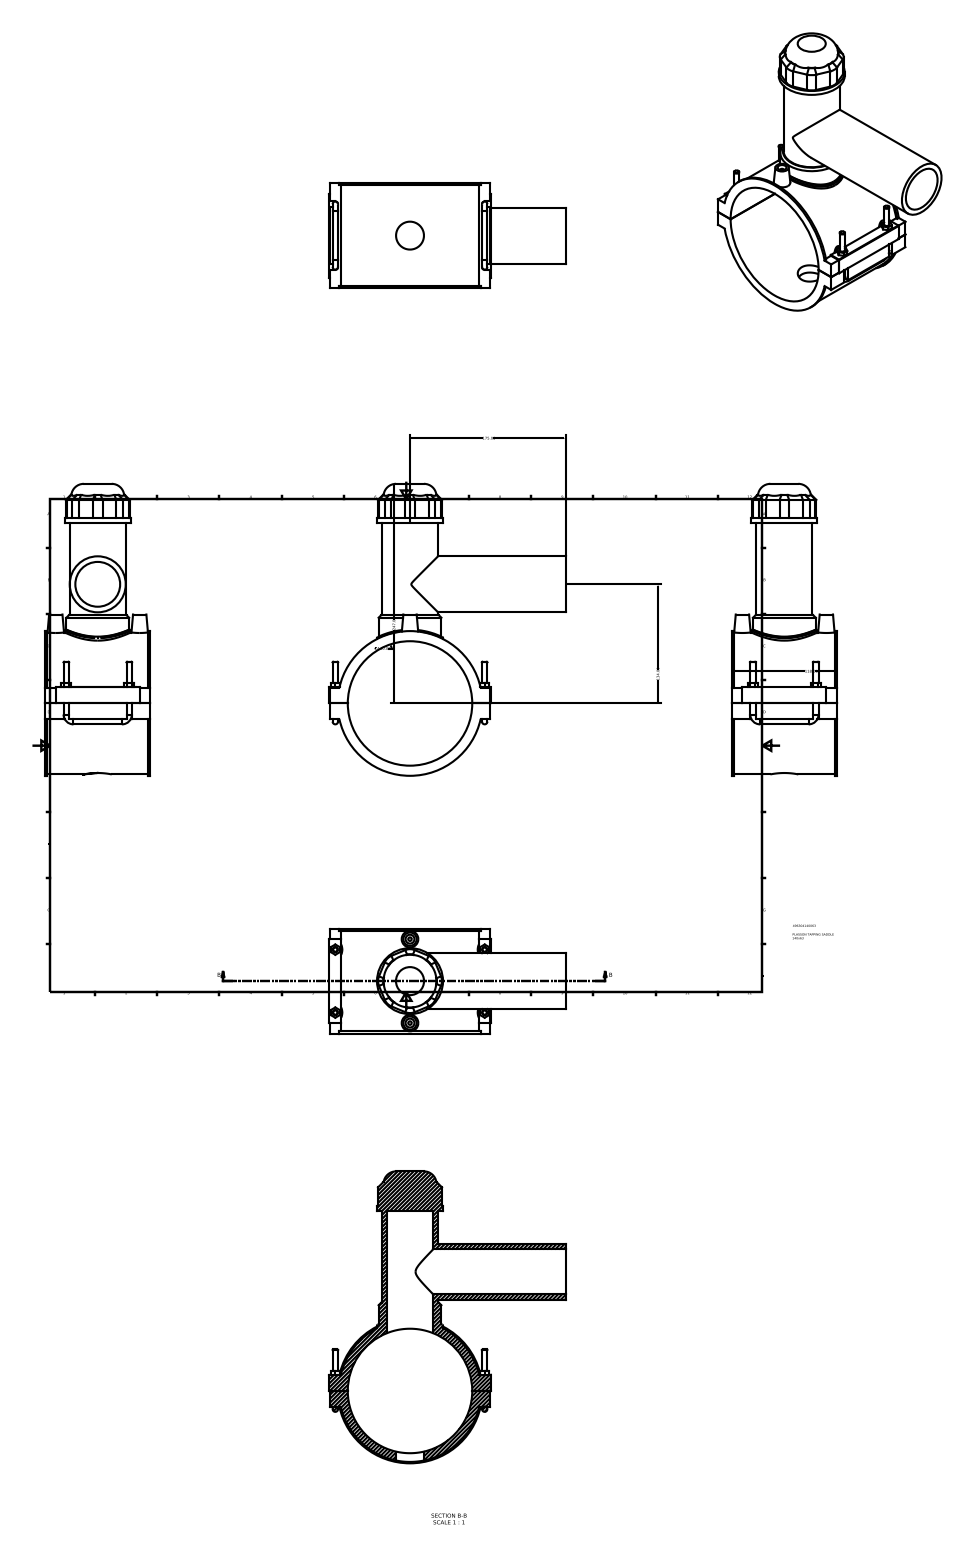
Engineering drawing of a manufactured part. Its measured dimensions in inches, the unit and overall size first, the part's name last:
Units: inches
Overall size (bounding box): 12.929 × 10.472 × 4.646
Round holes (diameter × count): ⌀0.394 ×2, ⌀1.235 ×1, ⌀1.984 ×1, ⌀2.045 ×1, ⌀5.512 ×1
Round bosses / shafts (diameter × count): ⌀0.236 ×6, ⌀0.157 ×2, ⌀6.409 ×1, ⌀6.283 ×1, ⌀2.921 ×1, ⌀2.775 ×1, ⌀2.483 ×1, ⌀2.48 ×1
Partial cylindrical surfaces — rounded edges, fillets, slot ends (radius × count): R0.551 ×8, R0.118 ×4, R0.295 ×4, R0.02 ×1, R3.267 ×1
Main face-to-face distances: 4.646, 0.039, 7.126, 7.984, 7.98, 0.687, 0.691, 8.671, 7.087, 1.417
Hole centre spacings: 1.858, 3.717
Volume: 65.84 in³ · Surface area: 397.9 in²
Bodies: 1 solid, 191 faces (118 planar, 48 cylindrical, 25 other)
Part name (STEP PRODUCT): 496304140063
STEP written by: Autodesk Inventor 2015 (AUTOMOTIVE_DESIGN)
